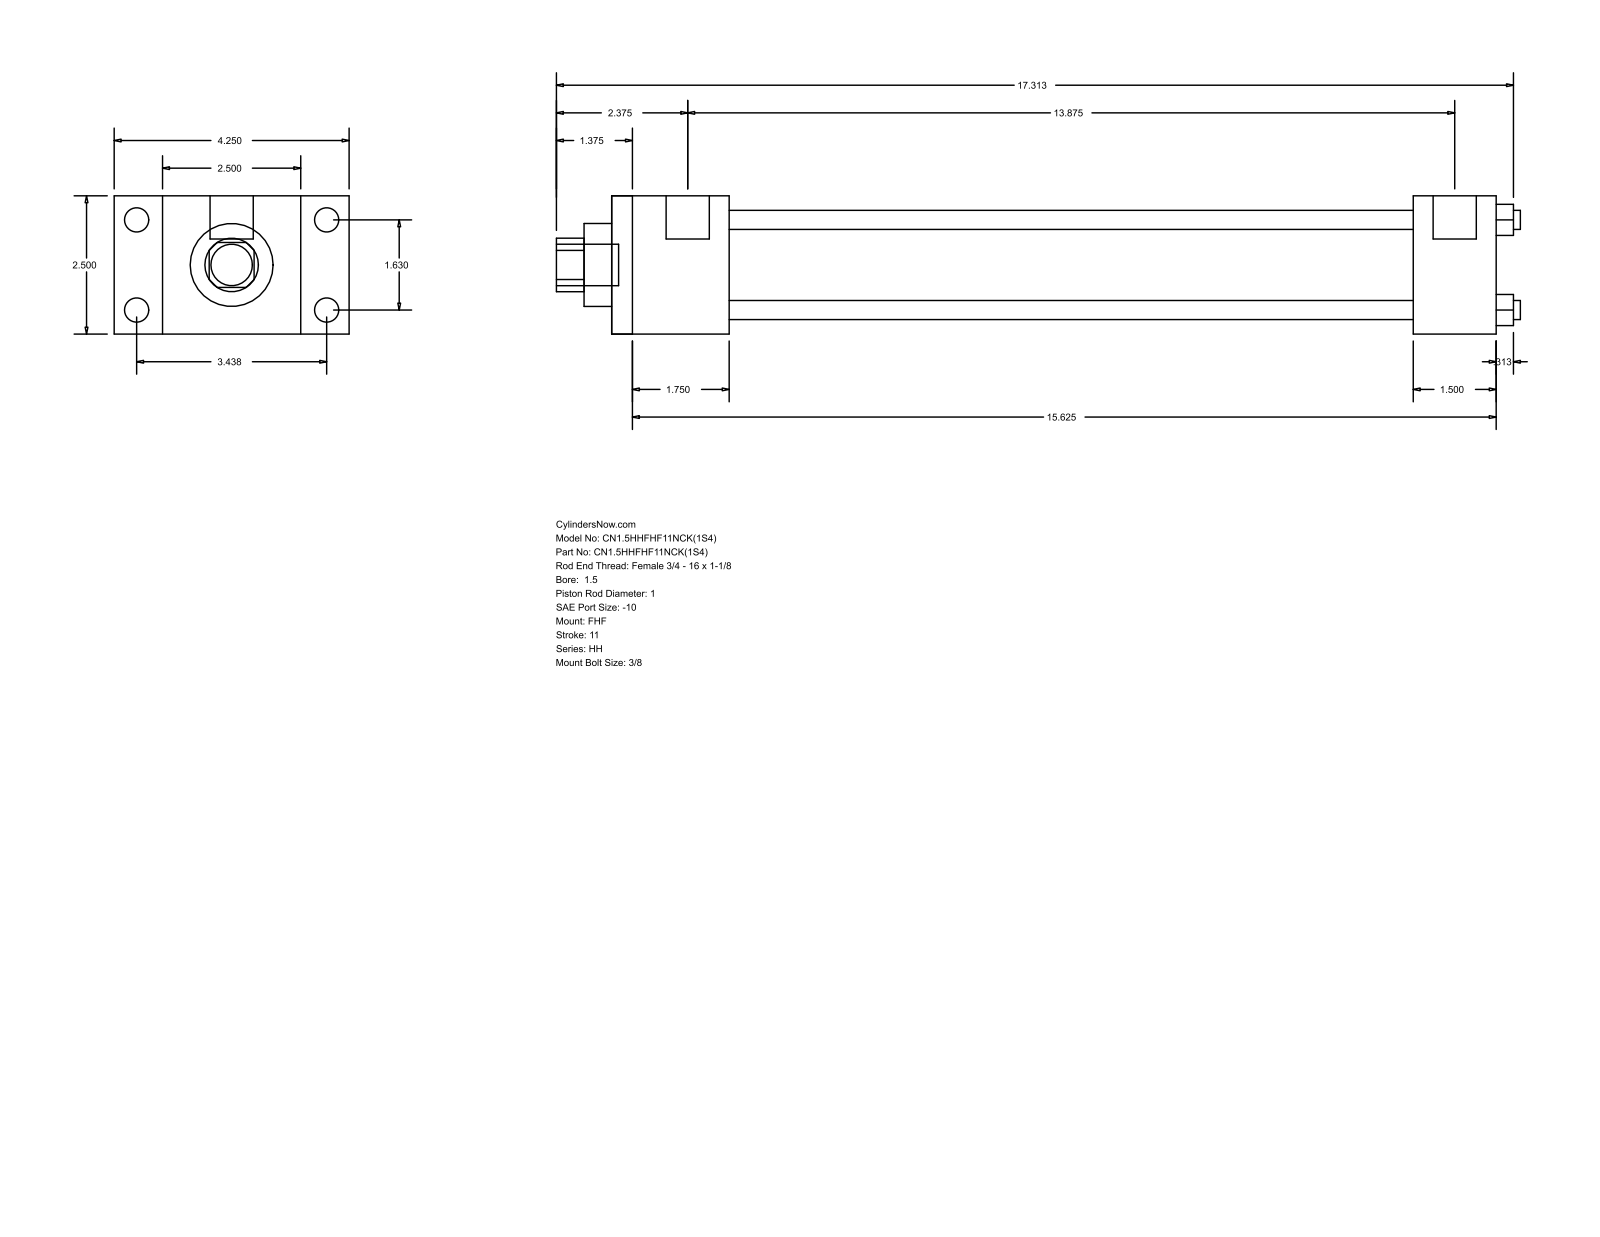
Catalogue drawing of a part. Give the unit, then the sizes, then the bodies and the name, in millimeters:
Units: millimetres
Overall size (bounding box): 442.91 × 107.95 × 63.5
Round holes (diameter × count): ⌀8.76 ×4, ⌀25.4 ×1, ⌀38.1 ×1, ⌀44.45 ×1
Round bosses / shafts (diameter × count): ⌀11.13 ×4, ⌀5.56 ×4, ⌀19.84 ×2, ⌀19.05 ×1
Partial cylindrical surfaces — rounded edges, fillets, slot ends (radius × count): R12.29 ×1
Main face-to-face distances: 63.5, 22.23, 85.73, 53.98, 107.96, 406.4, 352.42, 368.3, 314.32, 38.1
Hole centre spacings: 29.27, 41.4, 58.55
Bodies: 0 solids, 88 faces (60 planar, 28 cylindrical, 0 other)
Part name (STEP PRODUCT): HH_FHF__0150_1
STEP written by: GSSL Pune (CONFIG_CONTROL_DESIGN)
